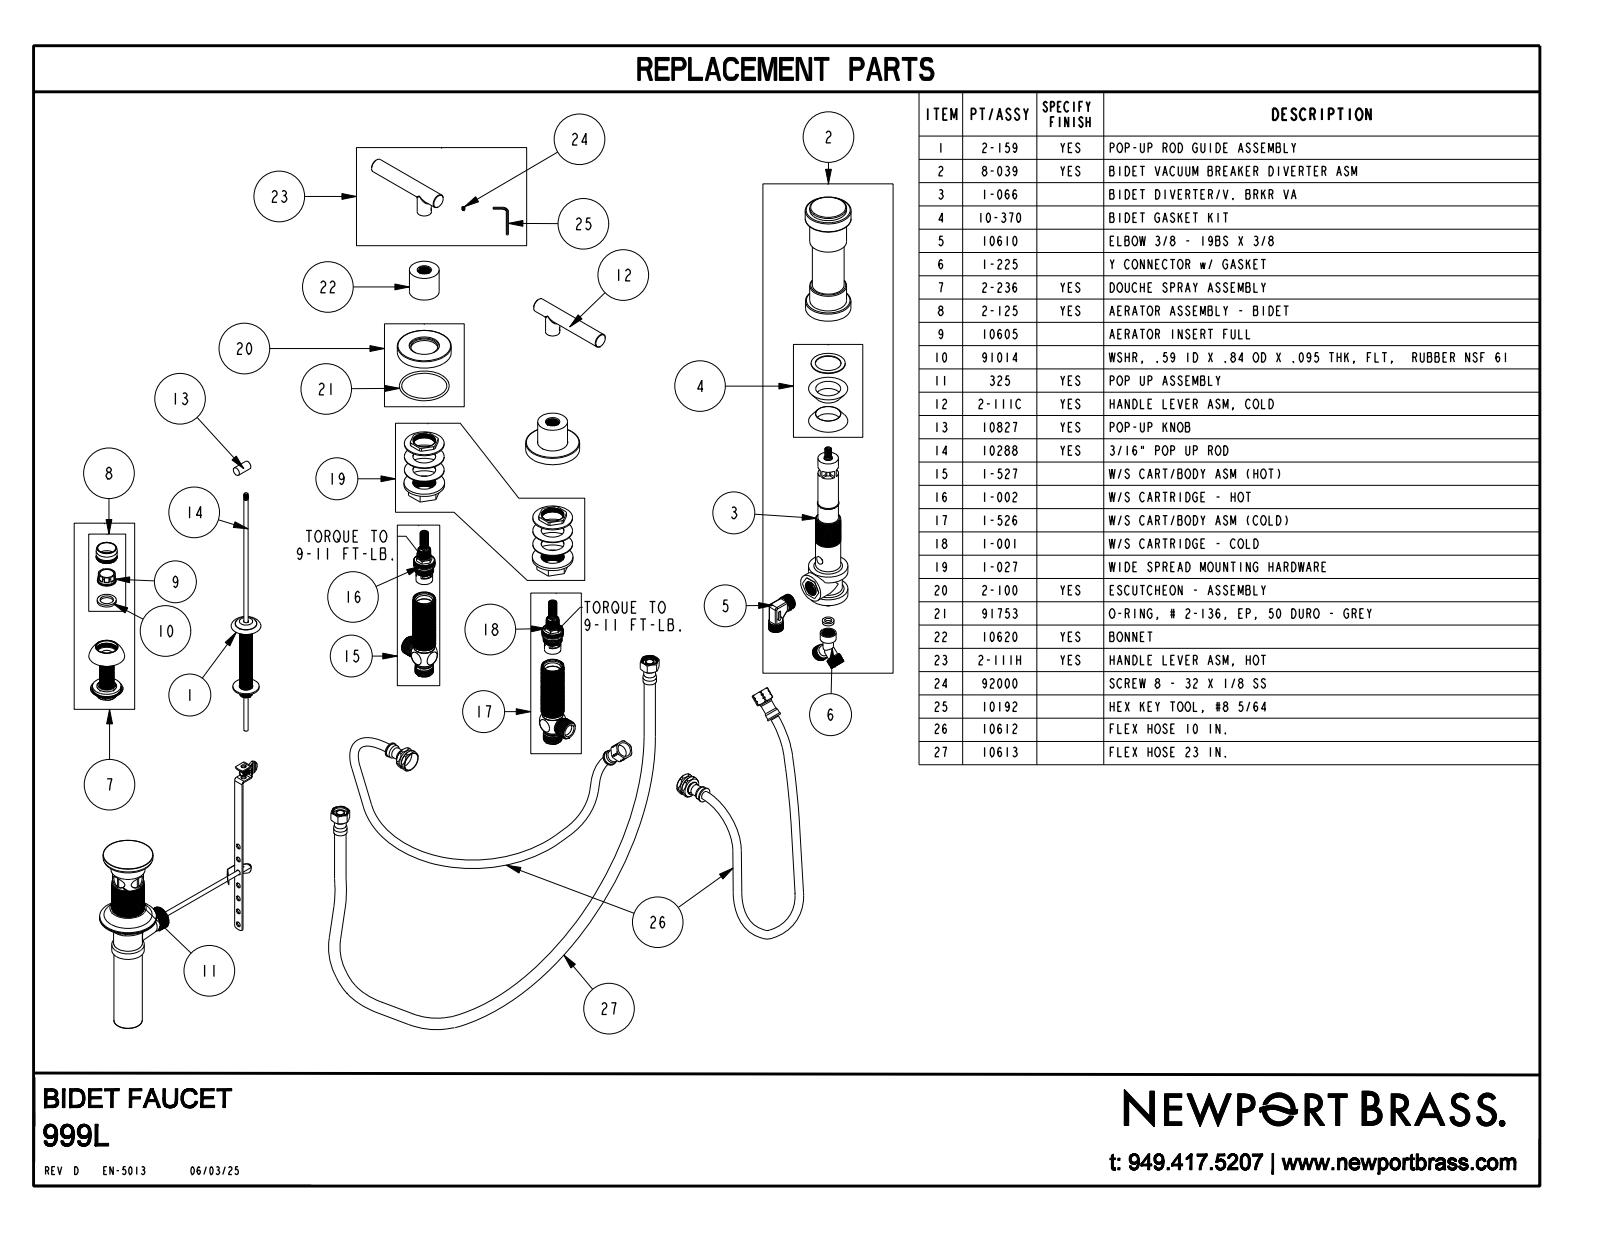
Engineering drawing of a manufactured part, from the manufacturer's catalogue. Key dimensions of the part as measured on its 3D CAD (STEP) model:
Part name (STEP PRODUCT): 999L
STEP written by: CREO PARAMETRIC BY PTC INC, 2018400 (CONFIG_CONTROL_DESIGN)
Units: inches
Bodies: 5 solids, 176 faces (50 planar, 64 cylindrical, 62 other)
Overall size (bounding box): 22.855 × 13.978 × 5.353
Volume: 21.22 in³ · Surface area: 98.89 in²
Round holes (diameter × count): ⌀0.625 ×1, ⌀0.792 ×1, ⌀0.94 ×1
Round bosses / shafts (diameter × count): ⌀0.625 ×3, ⌀2.375 ×2, ⌀1.313 ×2, ⌀0.4 ×2, ⌀2.025 ×1, ⌀1.52 ×1, ⌀0.925 ×1, ⌀0.775 ×1
Partial cylindrical surfaces — rounded edges, fillets, slot ends (radius × count): R0.21 ×8, R0.357 ×1, R1.077 ×1
Main face-to-face distances: 0.375, 1.108, 1.483, 3.468, 3.093, 1.985, 3.875, 10.103, 0.02, 1.503
